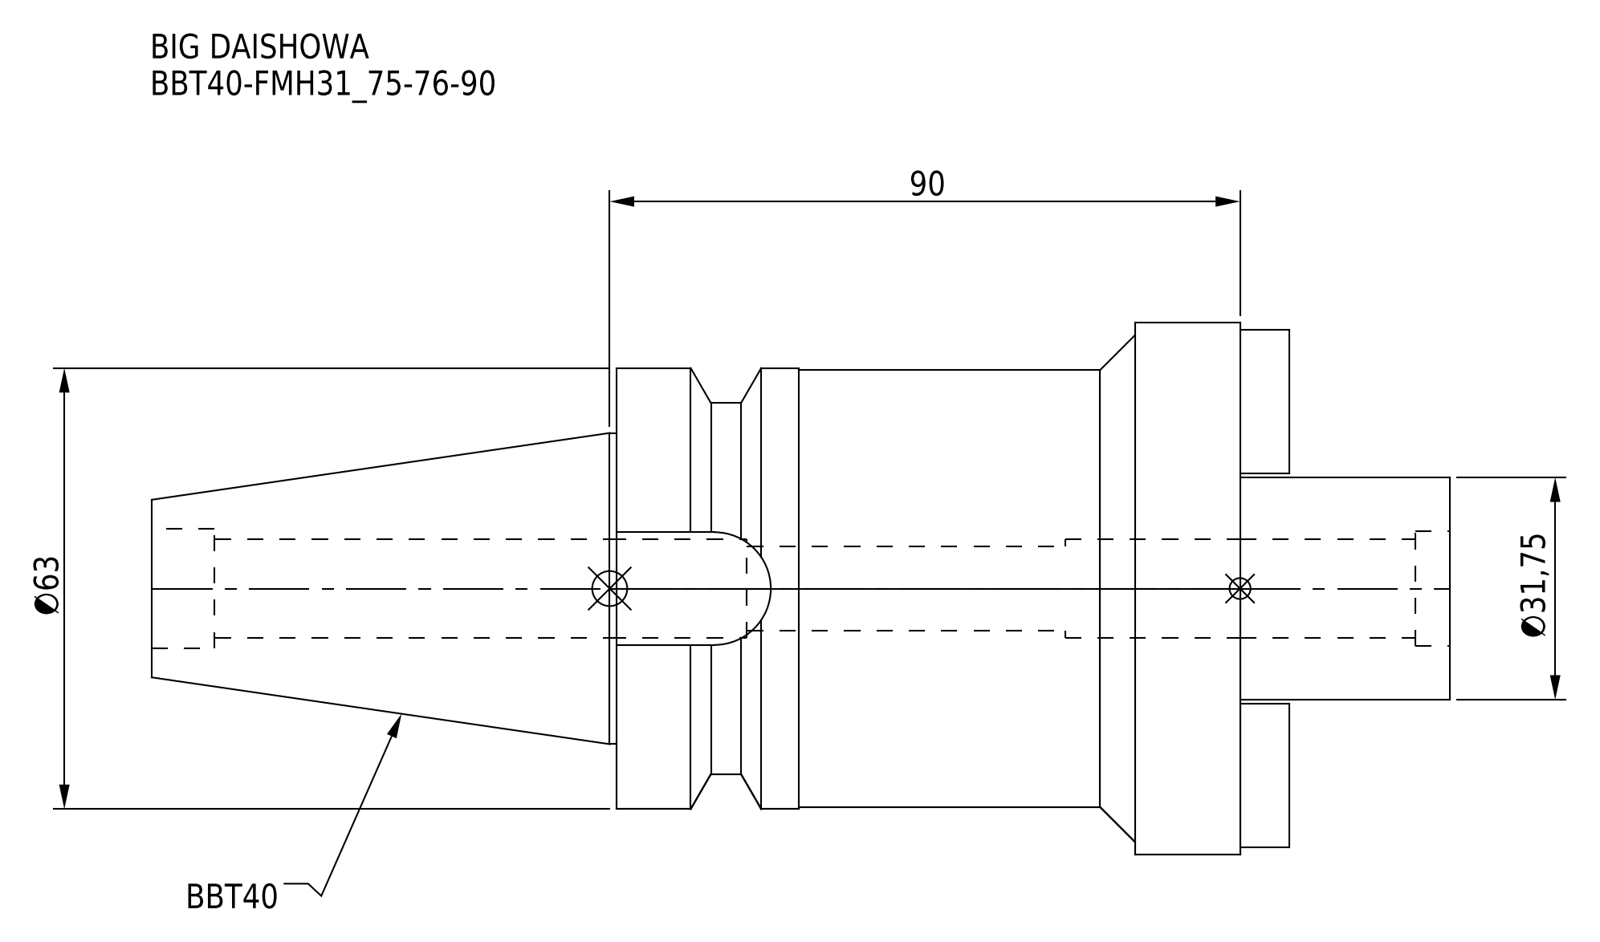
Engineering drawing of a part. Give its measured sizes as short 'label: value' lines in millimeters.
name: BBT40-FMH31_75-76-90
written by: CREO PARAMETRIC BY PTC INC, 2016380 (AUTOMOTIVE_DESIGN)
unit: mm
bodies: 1 solid, 64 faces (26 planar, 30 cylindrical, 8 other)
size: 185.4 × 76 × 76
volume: 352 416 mm³; area: 45 955 mm²
holes: 1× ⌀12, 1× ⌀14, 1× ⌀14.2, 1× ⌀16.5, 1× ⌀17
bosses: 1× ⌀76, 1× ⌀63, 1× ⌀62.4, 1× ⌀53, 1× ⌀44.45, 1× ⌀31.75
rounds: 1× R8.05
face distances: 89, 45, 30, 119, 16.15, 28.85, 23, 7, 96, 74
